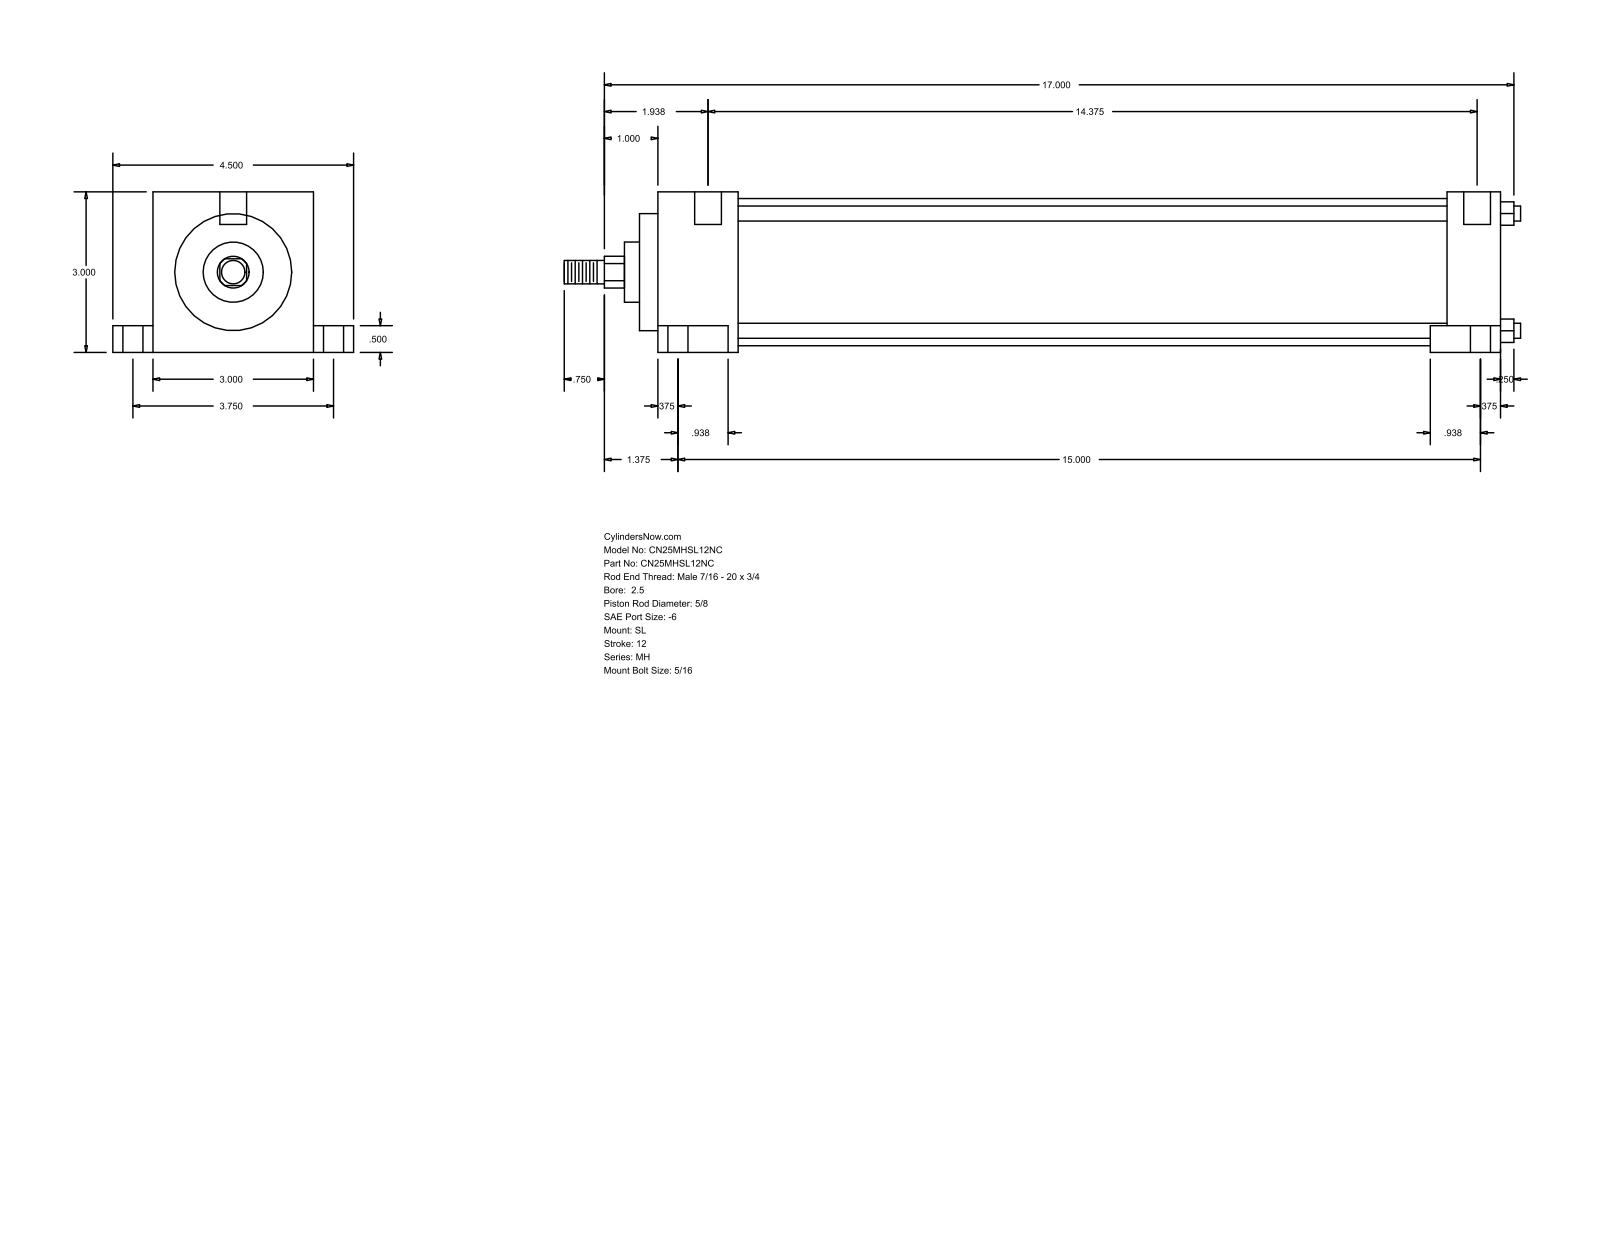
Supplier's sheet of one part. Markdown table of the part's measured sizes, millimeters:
| quantity | value |
| --- | --- |
| part name | MH_SL__0250_0.625 |
| STEP written by | GSSL Pune (CONFIG_CONTROL_DESIGN) |
| units | millimeters |
| bodies | 0 solids, 86 faces (61 planar, 25 cylindrical, 0 other) |
| overall size | 454.02 × 114.3 × 76.2 |
| round holes (diameter × count) | 5.56 × 2, 9.53 × 2, 15.88 × 2, 12.7 × 1 |
| round bosses / shafts (diameter × count) | 7.14 × 4, 69.85 × 1, 55.55 × 1, 28.57 × 1, 15.88 × 1, 11.11 × 1 |
| partial cylindrical surfaces (radius × count) | 7.54 × 1 |
| main face-to-face distances | 76.2, 25.4, 383.38, 408.78, 63.5, 12.7, 19.05, 95.25, 31.75, 375.44 |
| hole center spacings | 47.65, 3.17, 95.24 |
